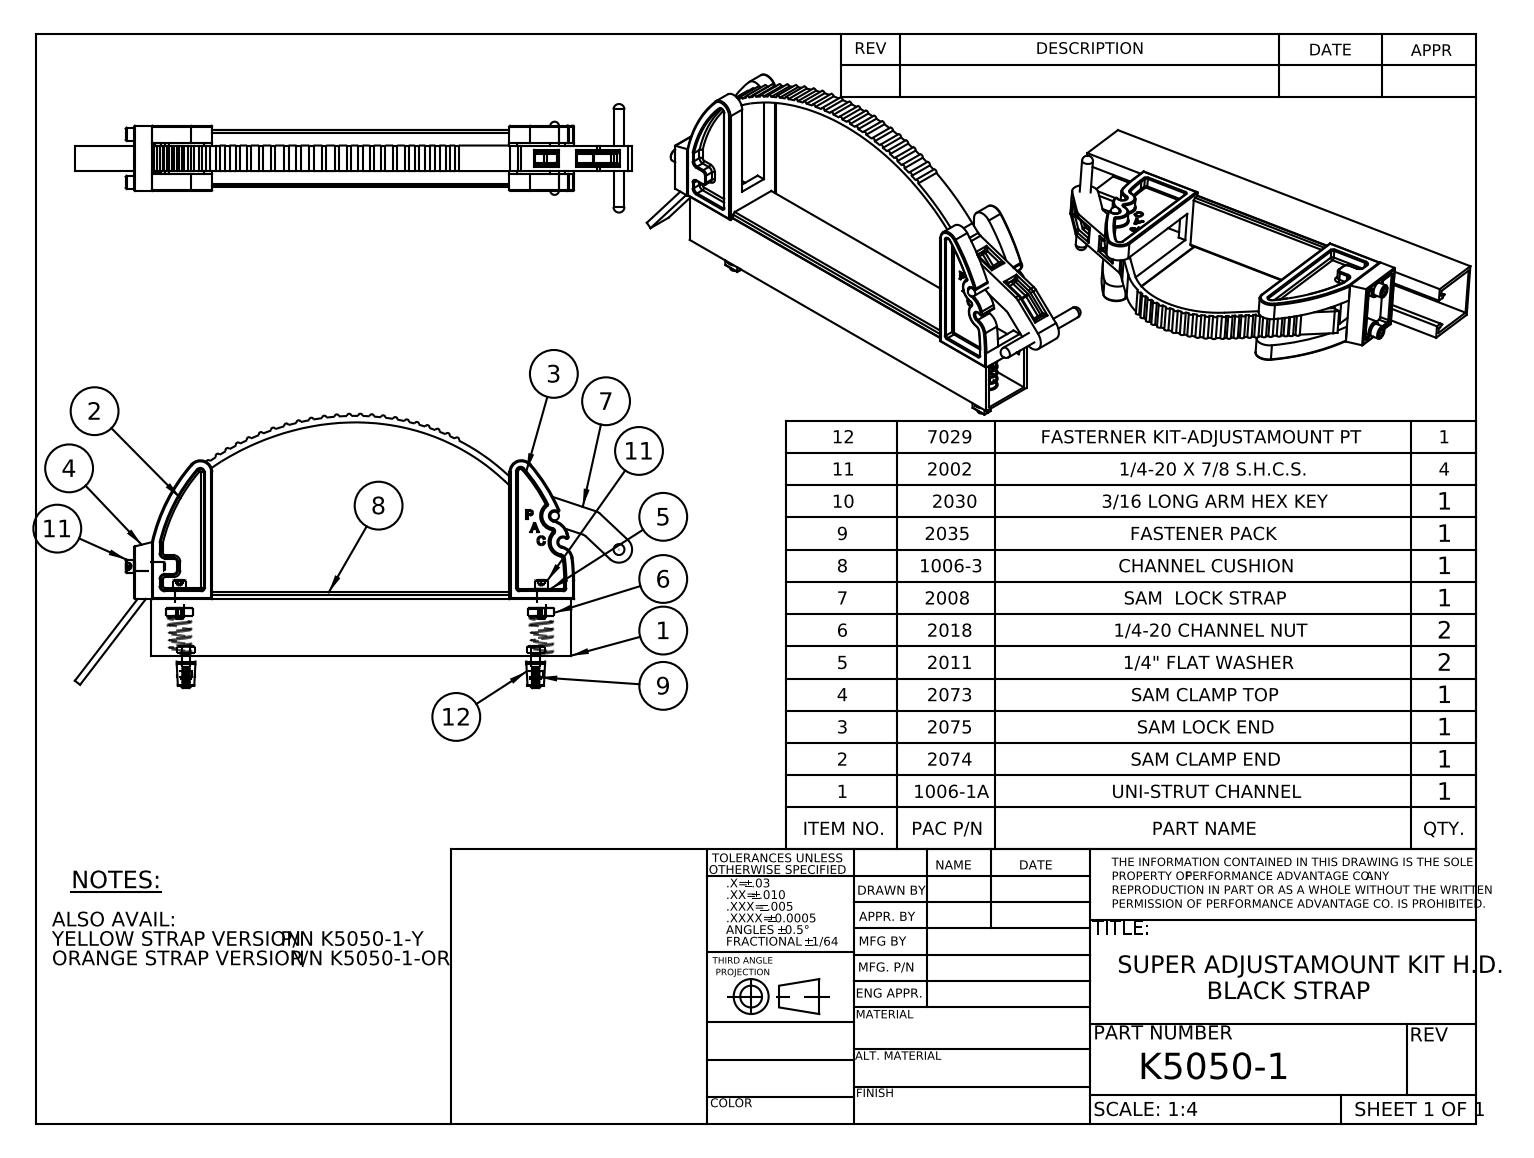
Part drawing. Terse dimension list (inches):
name: 2018_compressed; 7029; 1006-3; 2038_HBOLT 0.2500-20x1x1-N (+8 more)
written by: SolidWorks 2014 (CONFIG_CONTROL_DESIGN)
unit: in
bodies: 26 solids, 1472 faces (459 planar, 432 cylindrical, 581 other)
size: 15.936 × 7.845 × 3.106
volume: 27.75 in³; area: 362.9 in²
holes: 6× ⌀0.201, 2× ⌀0.25, 2× ⌀0.266, 2× ⌀0.269, 2× ⌀0.288, 2× ⌀0.313
bosses: 5× ⌀0.25, 4× ⌀0.375, 2× ⌀0.625, 2× ⌀0.404, 2× ⌀0.375, 2× ⌀0.187, 1× ⌀0.313
rounds: 51× R0.063, 34× R0.062, 32× R0.031, 12× R0.062, 8× R0.03, 8× R0.06, 7× R0.125, 6× R0.09
face distances: 1.625, 0.109, 1.516, 1.25, 0.188, 0.375, 0.266, 1.141, 1.407, 0.078
hole spacings: 0.161, 0.187, 1.375, 10, 10.161, 10.187, 10.348
